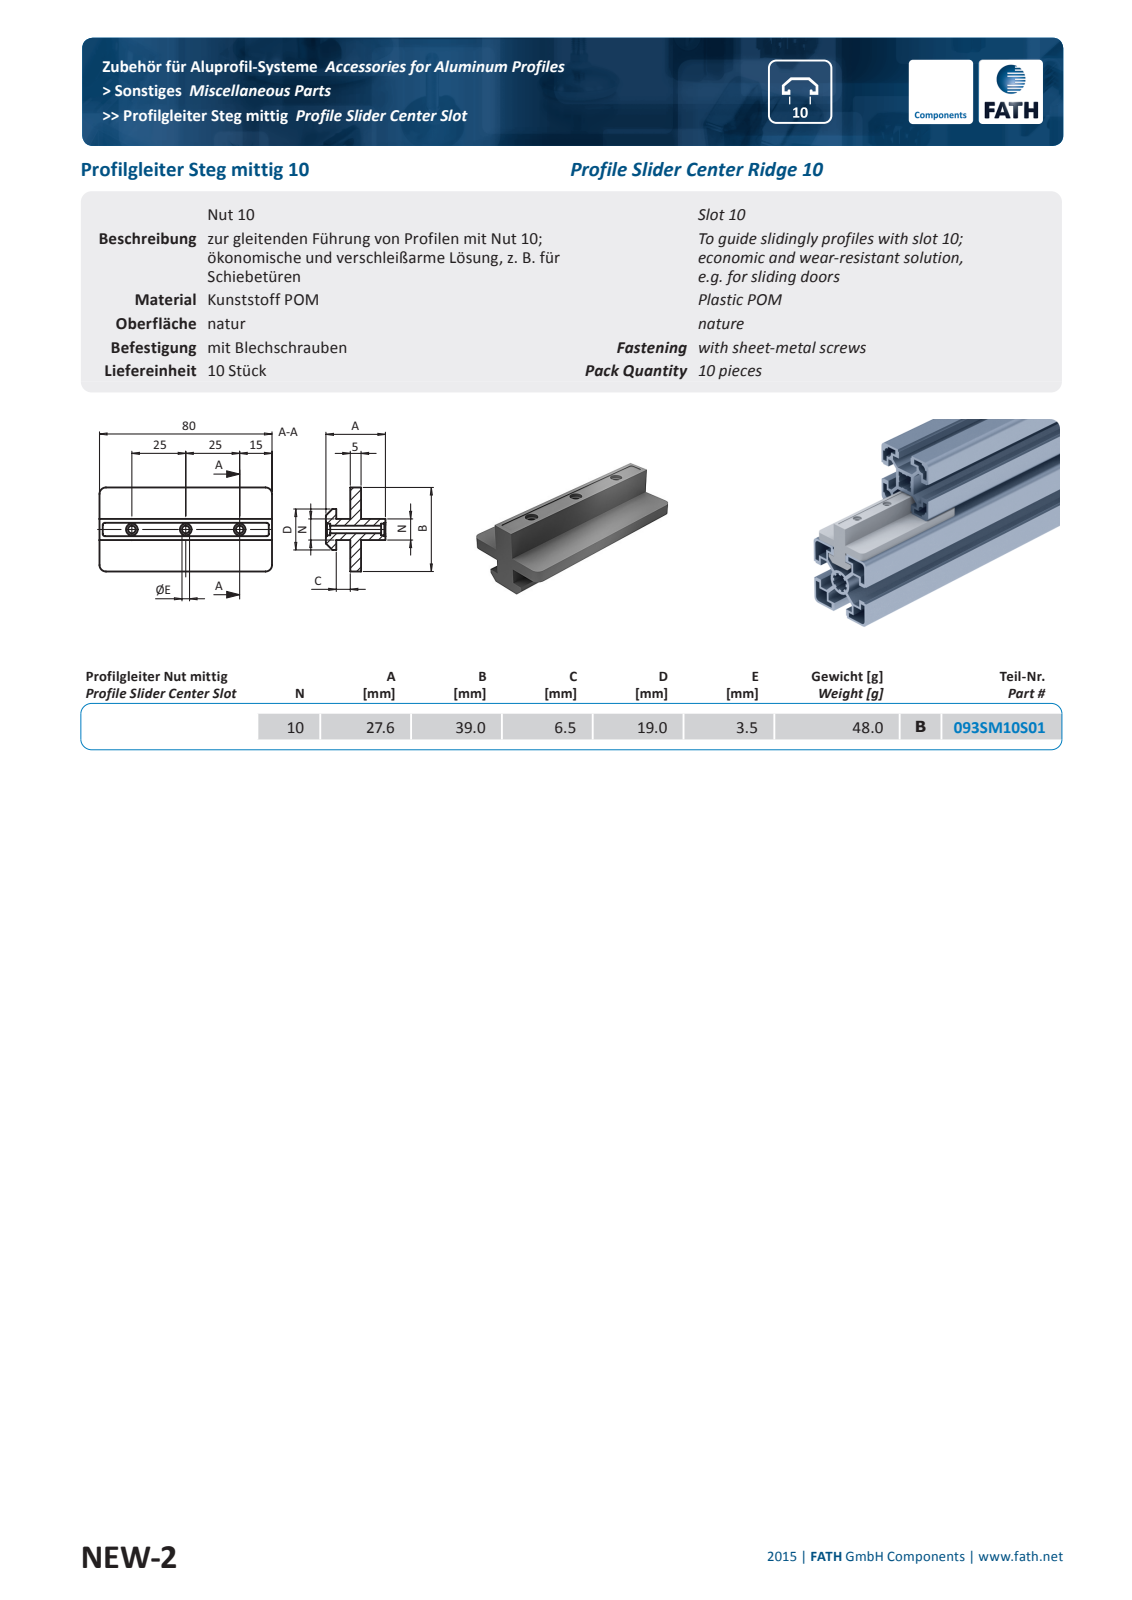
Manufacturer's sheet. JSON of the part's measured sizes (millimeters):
{"part_name": "fath_093sm10s01", "step_written_by": "Spatial InterOp 3D (automotive_design)", "units": "millimeters", "bodies": {"solids": 1, "faces": 66, "planar": 36, "cylindrical": 30, "other": 0}, "overall_size": [80, 39, 27.6], "volume_mm3": 34729, "surface_area_mm2": 13747, "round_holes": [[3.5, 3], [5.4, 3]], "partial_cylinders_radius": [[1, 4], [3, 4]], "face_to_face_distances": [5, 9.8, 11.3, 16.3, 10.8, 15.8, 14.6, 24.4, 6.5, 11.5], "hole_center_spacings": [25, 50]}
